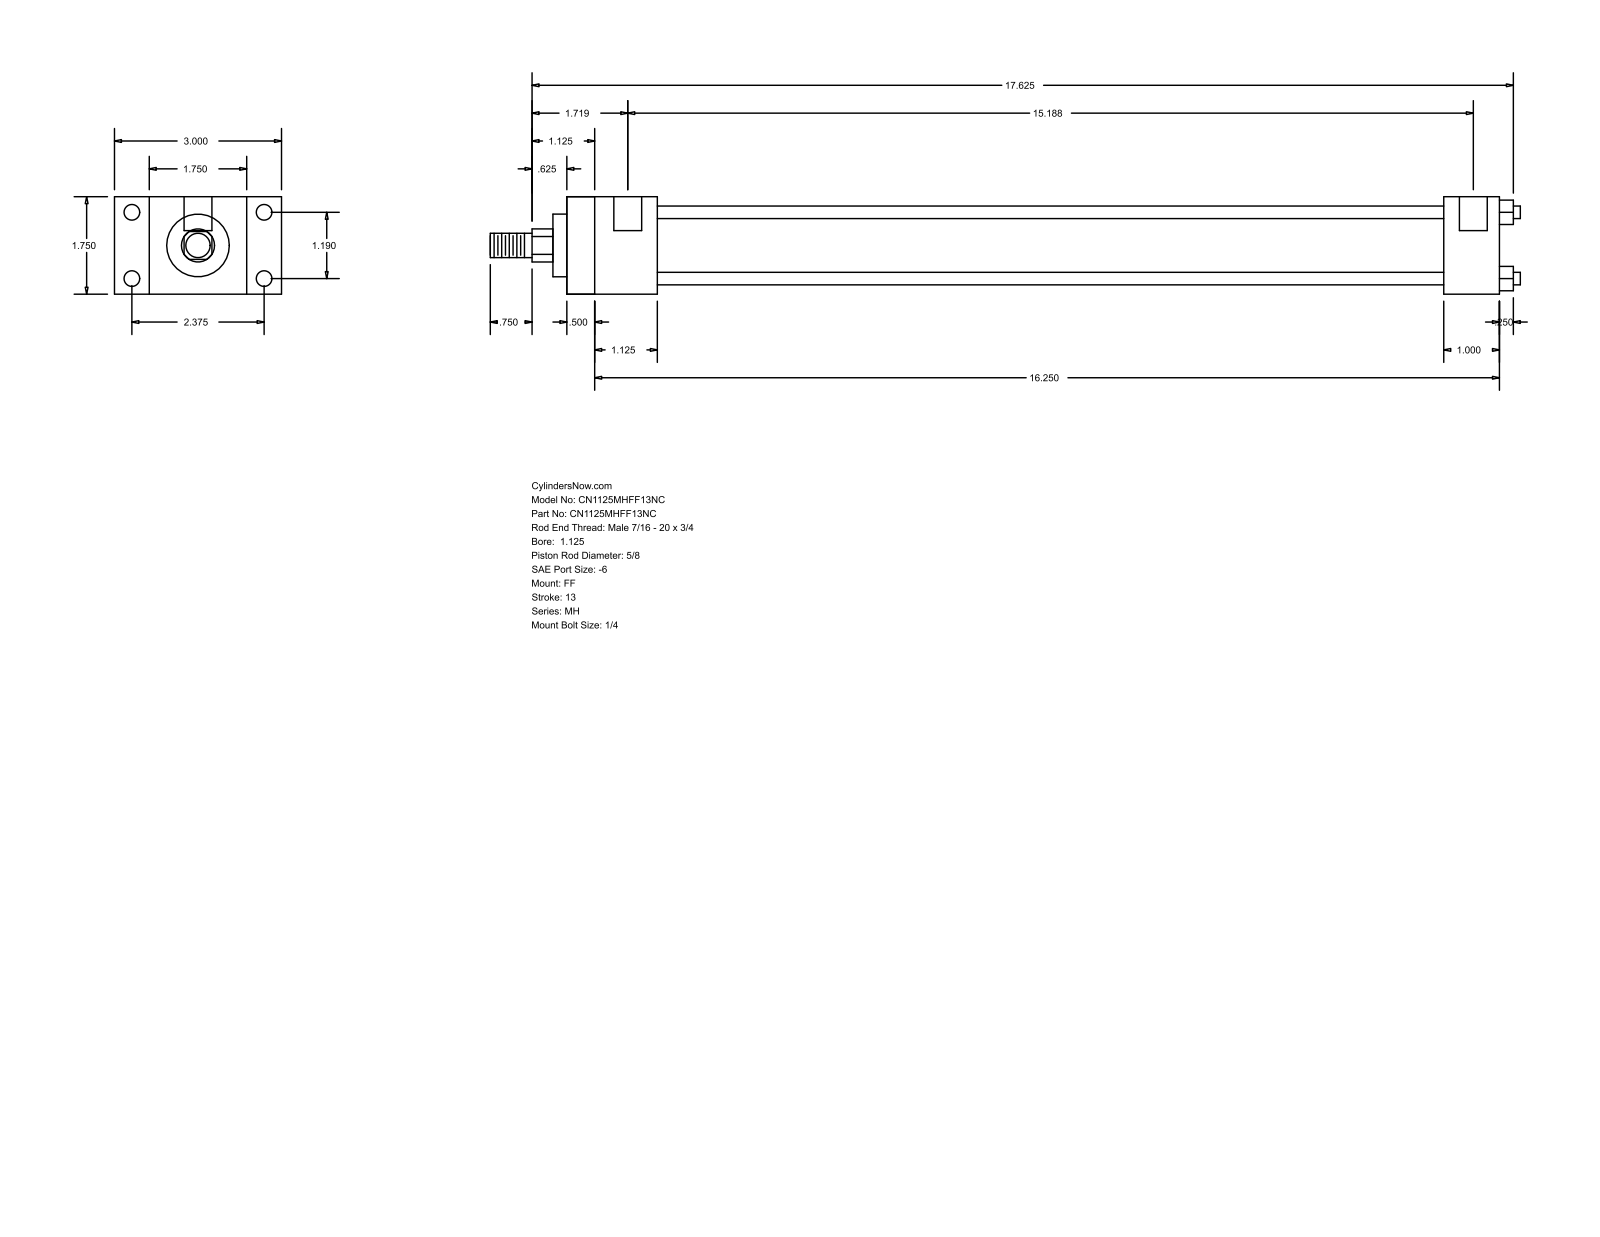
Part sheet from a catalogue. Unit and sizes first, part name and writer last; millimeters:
Units: millimetres
Overall size (bounding box): 469.9 × 76.2 × 44.45
Round holes (diameter × count): ⌀5.56 ×4, ⌀7.14 ×4, ⌀12.7 ×2
Round bosses / shafts (diameter × count): ⌀5.71 ×4, ⌀34.92 ×1, ⌀28.57 ×1, ⌀15.88 ×1, ⌀11.11 ×1
Partial cylindrical surfaces — rounded edges, fillets, slot ends (radius × count): R7.54 ×1
Main face-to-face distances: 44.46, 425.44, 15.87, 12.69, 412.75, 28.58, 60.33, 41.27, 400.05, 387.36
Hole centre spacings: 30.22, 60.32, 67.47, 382.59, 3.17, 385.76
Bodies: 0 solids, 92 faces (64 planar, 28 cylindrical, 0 other)
Part name (STEP PRODUCT): MH_FF__0112_0.625
STEP written by: GSSL Pune (CONFIG_CONTROL_DESIGN)
